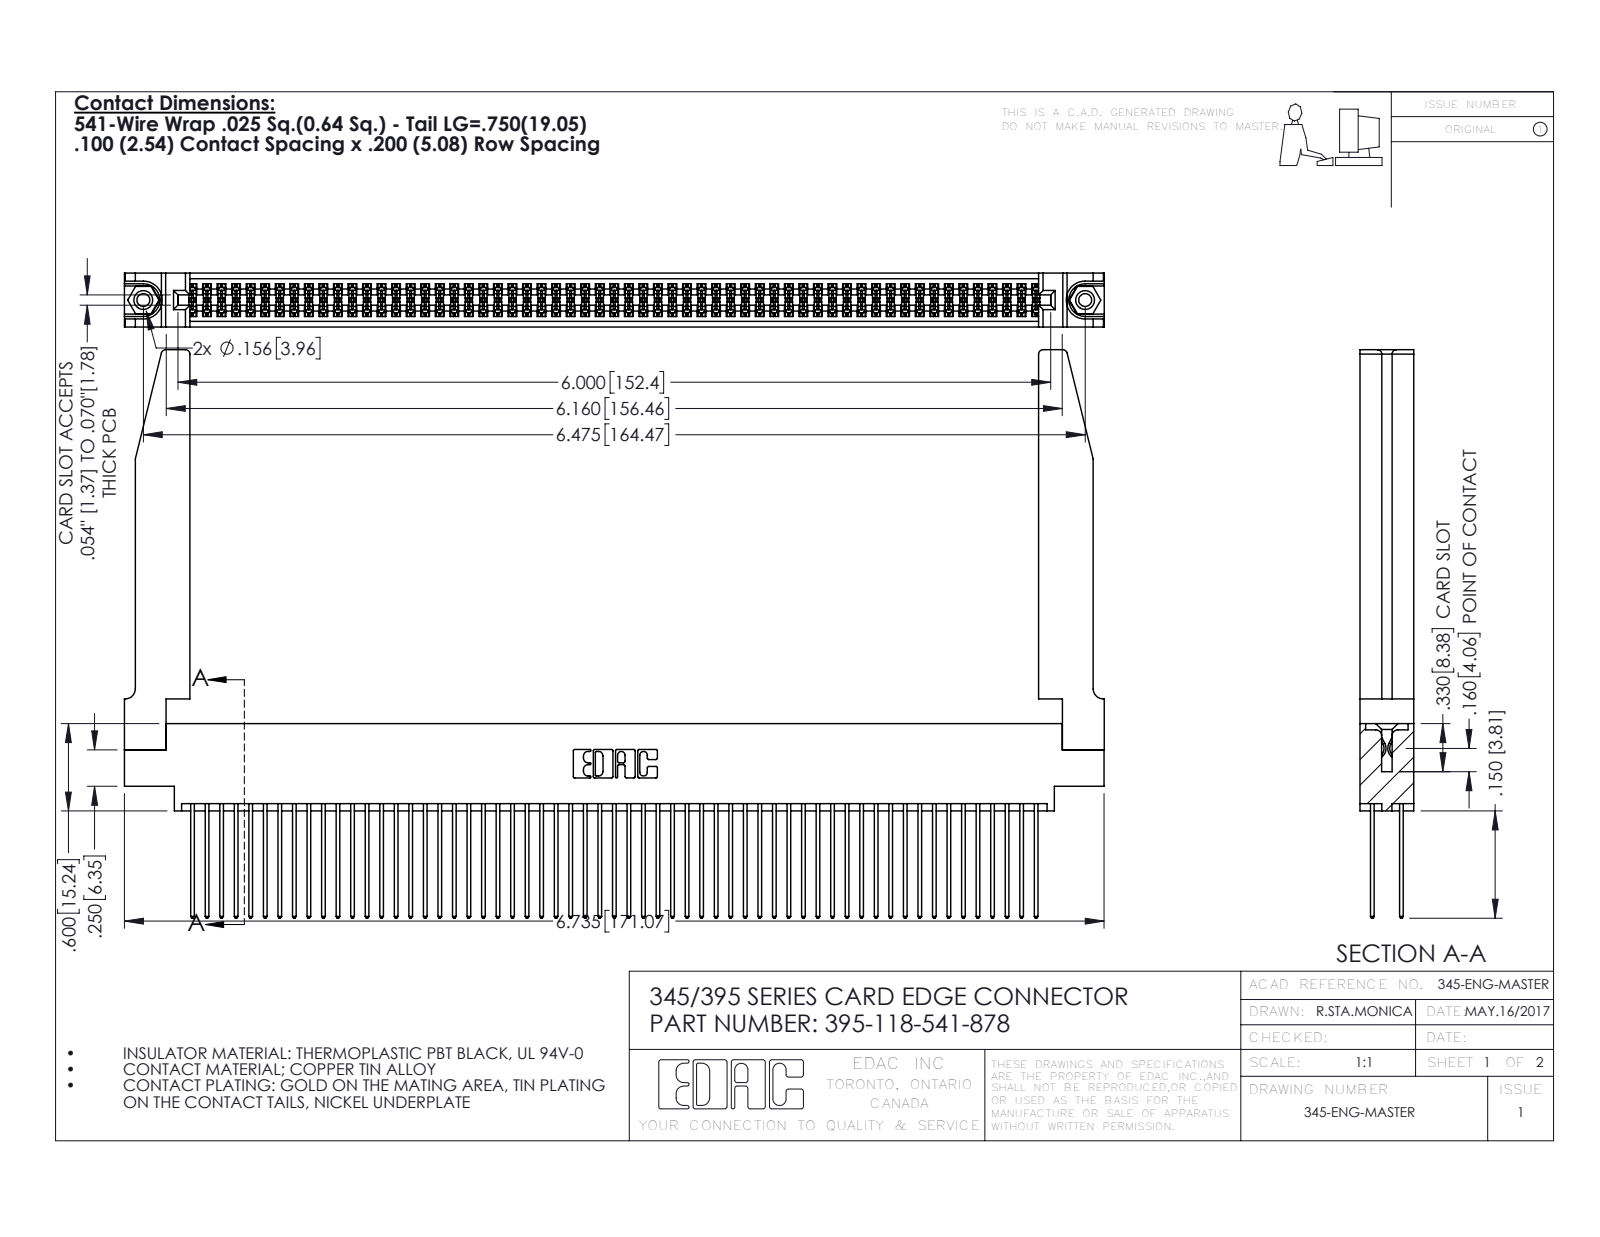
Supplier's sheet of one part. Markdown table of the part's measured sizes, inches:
| quantity | value |
| --- | --- |
| part name | 345-292-001_345-293-141; 345-220-078_345-220-078; 395-118-541-878; 345-250-001_345-250-001-102 (+1 more) |
| STEP written by | SolidWorks 2016 (CONFIG_CONTROL_DESIGN) |
| units | inches |
| bodies | 123 solids, 6264 faces (4120 planar, 2092 cylindrical, 52 other) |
| overall size | 6.736 × 3.907 × 0.37 |
| volume | 1.532 in³ |
| surface area | 56 in² |
| round holes (diameter × count) | 0.089 × 2, 0.125 × 2, 0.156 × 2, 0.064 × 1 |
| round bosses / shafts (diameter × count) | 0.155 × 2 |
| partial cylindrical surfaces (radius × count) | 0.006 × 177, 0.01 × 118, 0.01 × 22, 0.03 × 8, 0.007 × 6, 0.031 × 6, 0.026 × 3, 0.014 × 2 |
| main face-to-face distances | 0.072, 0.298, 0.37, 0.098, 0.272, 0.025, 0.2, 0.225, 0.175, 0.148 |
| hole center spacings | 0.27, 6.239, 6.475 |
